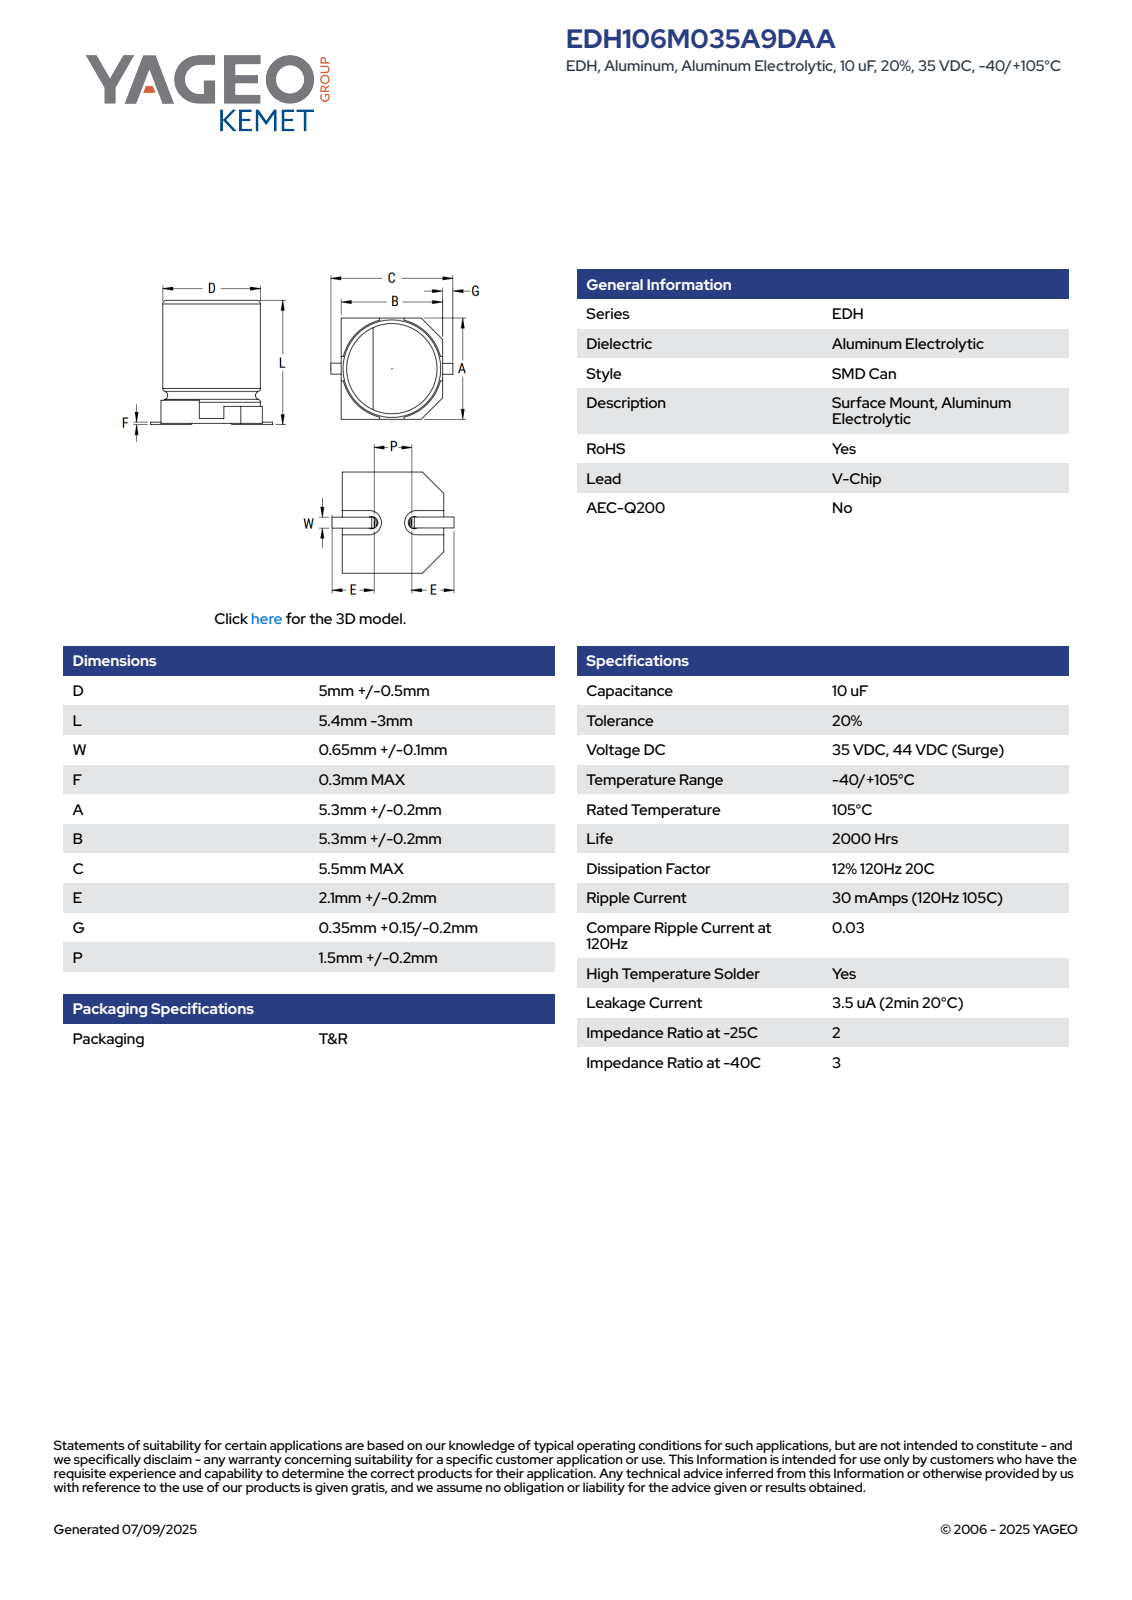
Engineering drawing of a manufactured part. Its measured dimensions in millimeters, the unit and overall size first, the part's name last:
Units: millimetres
Overall size (bounding box): 6.3 × 5.5 × 2.4
Round bosses / shafts (diameter × count): ⌀5.26 ×1
Partial cylindrical surfaces — rounded edges, fillets, slot ends (radius × count): R0.2 ×2, R2.18 ×1, R2.75 ×1
Main face-to-face distances: 2.1, 1.98, 1.5, 0.42, 2.4, 0.9, 0.6, 0.48, 0.4, 5.5
Volume: 49 mm³ · Surface area: 151 mm²
Bodies: 5 solids, 78 faces (61 planar, 11 cylindrical, 6 other)
Part name (STEP PRODUCT): CAC_S_5X5.4_D5.5L5.65W0.75F0.3A5.5B5.5C5.5E2.4P1.7
STEP written by: SolidWorks 2021 (AUTOMOTIVE_DESIGN)
